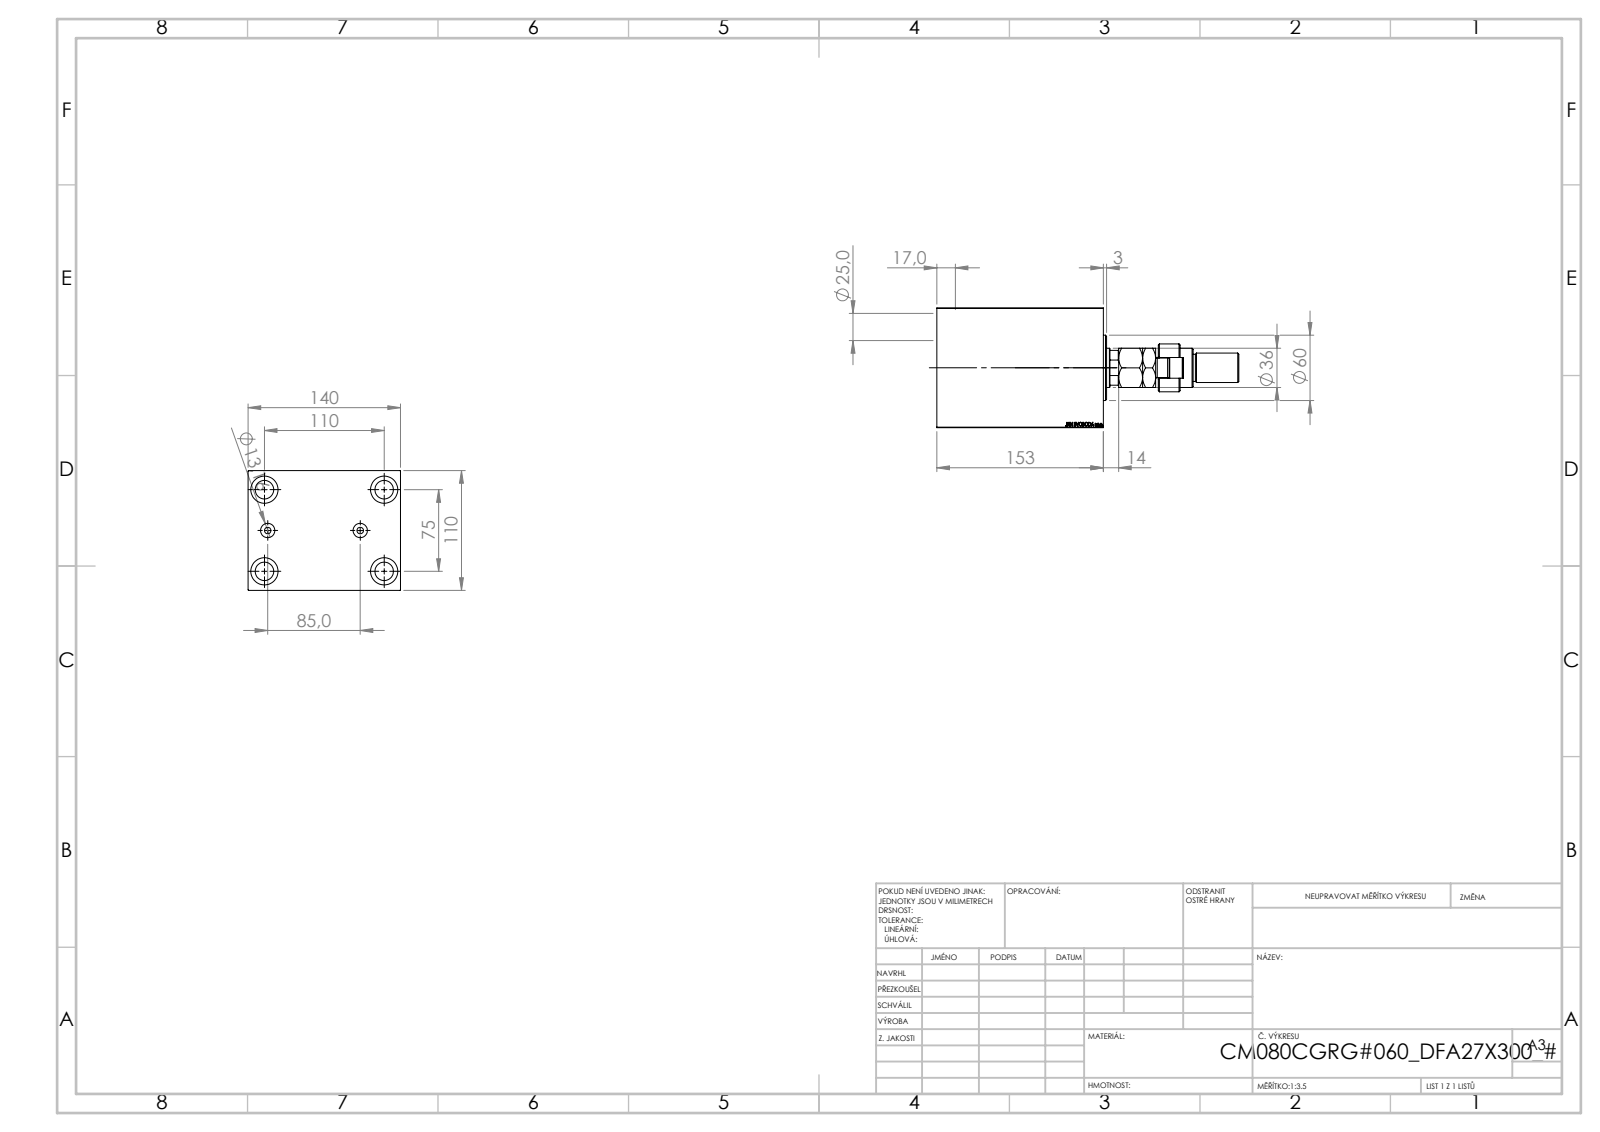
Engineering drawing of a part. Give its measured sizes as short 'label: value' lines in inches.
name: MFA; FEMALE_PART_FOR_DFA; V450CM_C_Body; V450CM_C_VCP (+1 more)
written by: SolidWorks 2019 (CONFIG_CONTROL_DESIGN)
unit: in
bodies: 5 solids, 948 faces (439 planar, 71 cylindrical, 438 other)
size: 10.886 × 5.512 × 4.331
volume: 136 in³; area: 344.1 in²
holes: 4× ⌀0.669, 4× ⌀0.984, 2× ⌀0.236, 2× ⌀0.518, 1× ⌀1.004, 1× ⌀1.555, 1× ⌀3.15, 1× ⌀3.228, 1× ⌀3.425
bosses: 1× ⌀2.362, 1× ⌀1.732, 1× ⌀1.417, 1× ⌀1.102, 1× ⌀1.063, 1× ⌀0.984, 1× ⌀0.709
rounds: 1× R0.374, 1× R0.591, 1× R0.689
face distances: 4.331, 5.512, 2.008, 6.024, 4.016, 0.394, 0.85, 1.157, 5.173, 4.78
hole spacings: 1.556, 2.621, 4.113, 1.673, 2.953, 4.331, 5.242, 3.346
